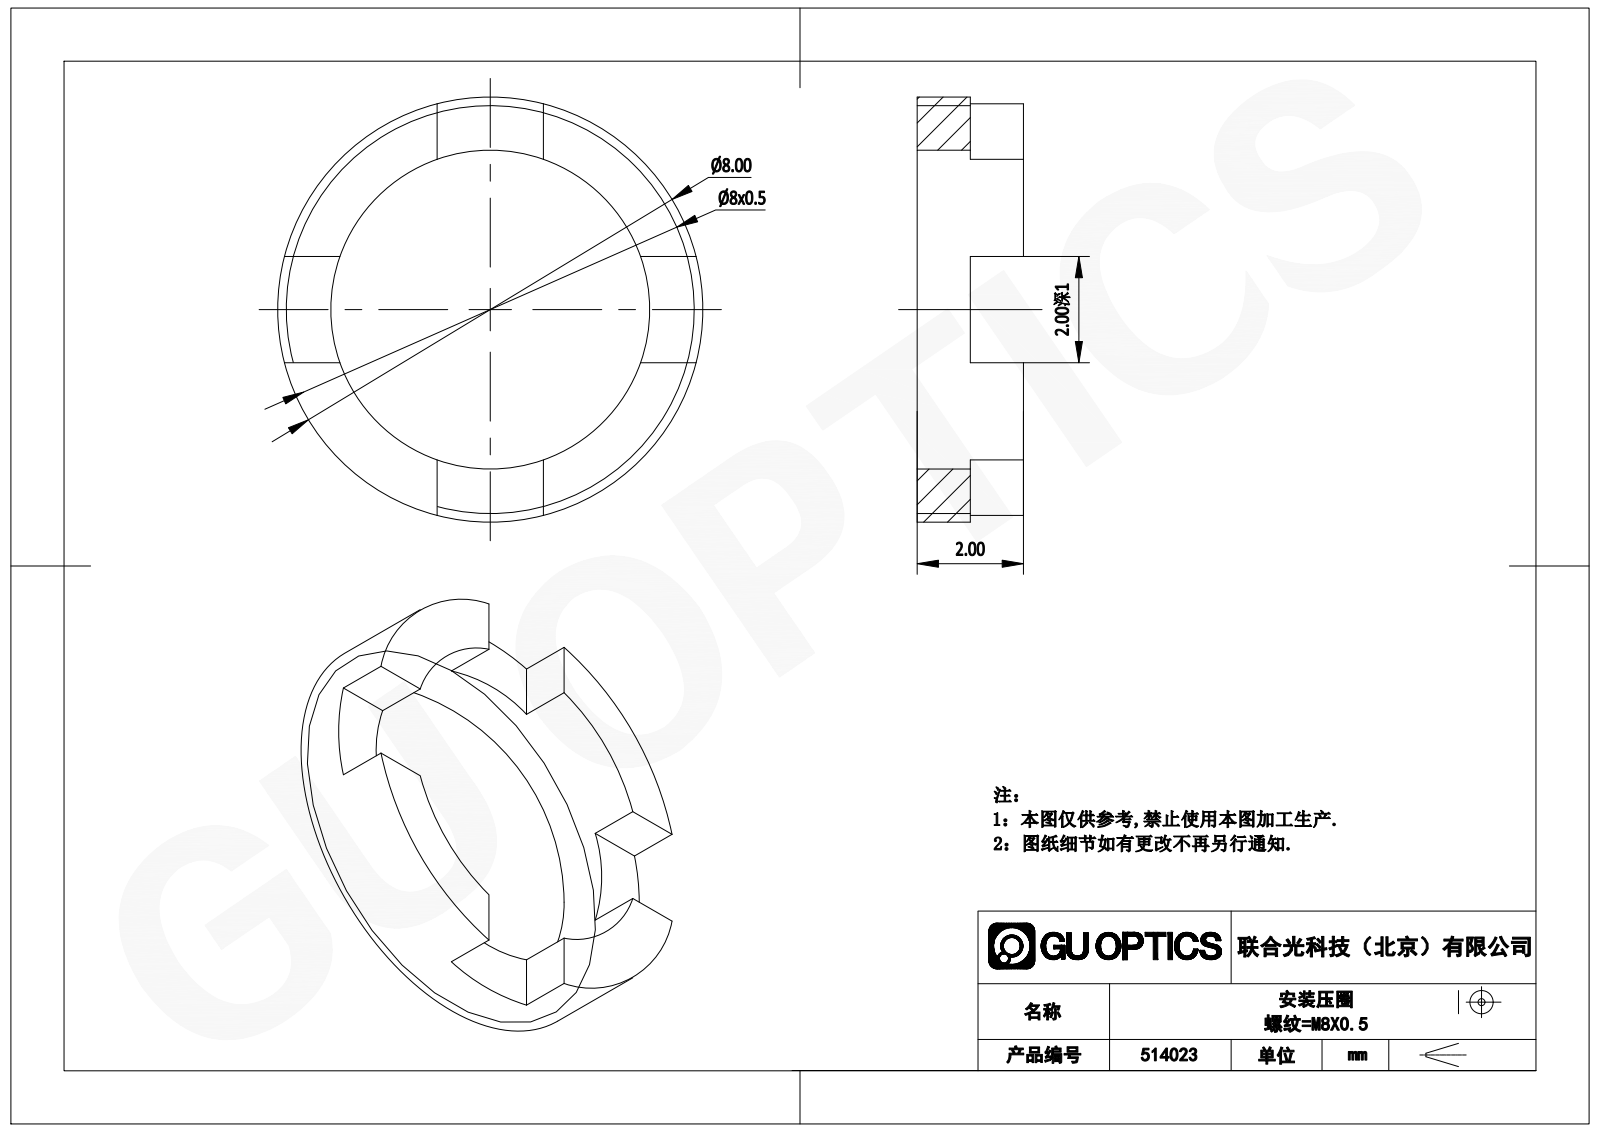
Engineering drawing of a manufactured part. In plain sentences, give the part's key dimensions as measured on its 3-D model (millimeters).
The part is named "514023". Its 3-D file was written by "SolidWorks 2020 (CONFIG_CONTROL_DESIGN)". It is 1 solid with 21 faces: 17 planar, 4 cylindrical and 0 other. Overall it measures 8 by 8 by 2 millimeters. Its volume is 36 cubic millimeters and its surface area 124 square millimeters. Round holes: 1 of diameter 6. Round bosses or shafts: 1 of diameter 8. The main face-to-face distances are 2, 1.
